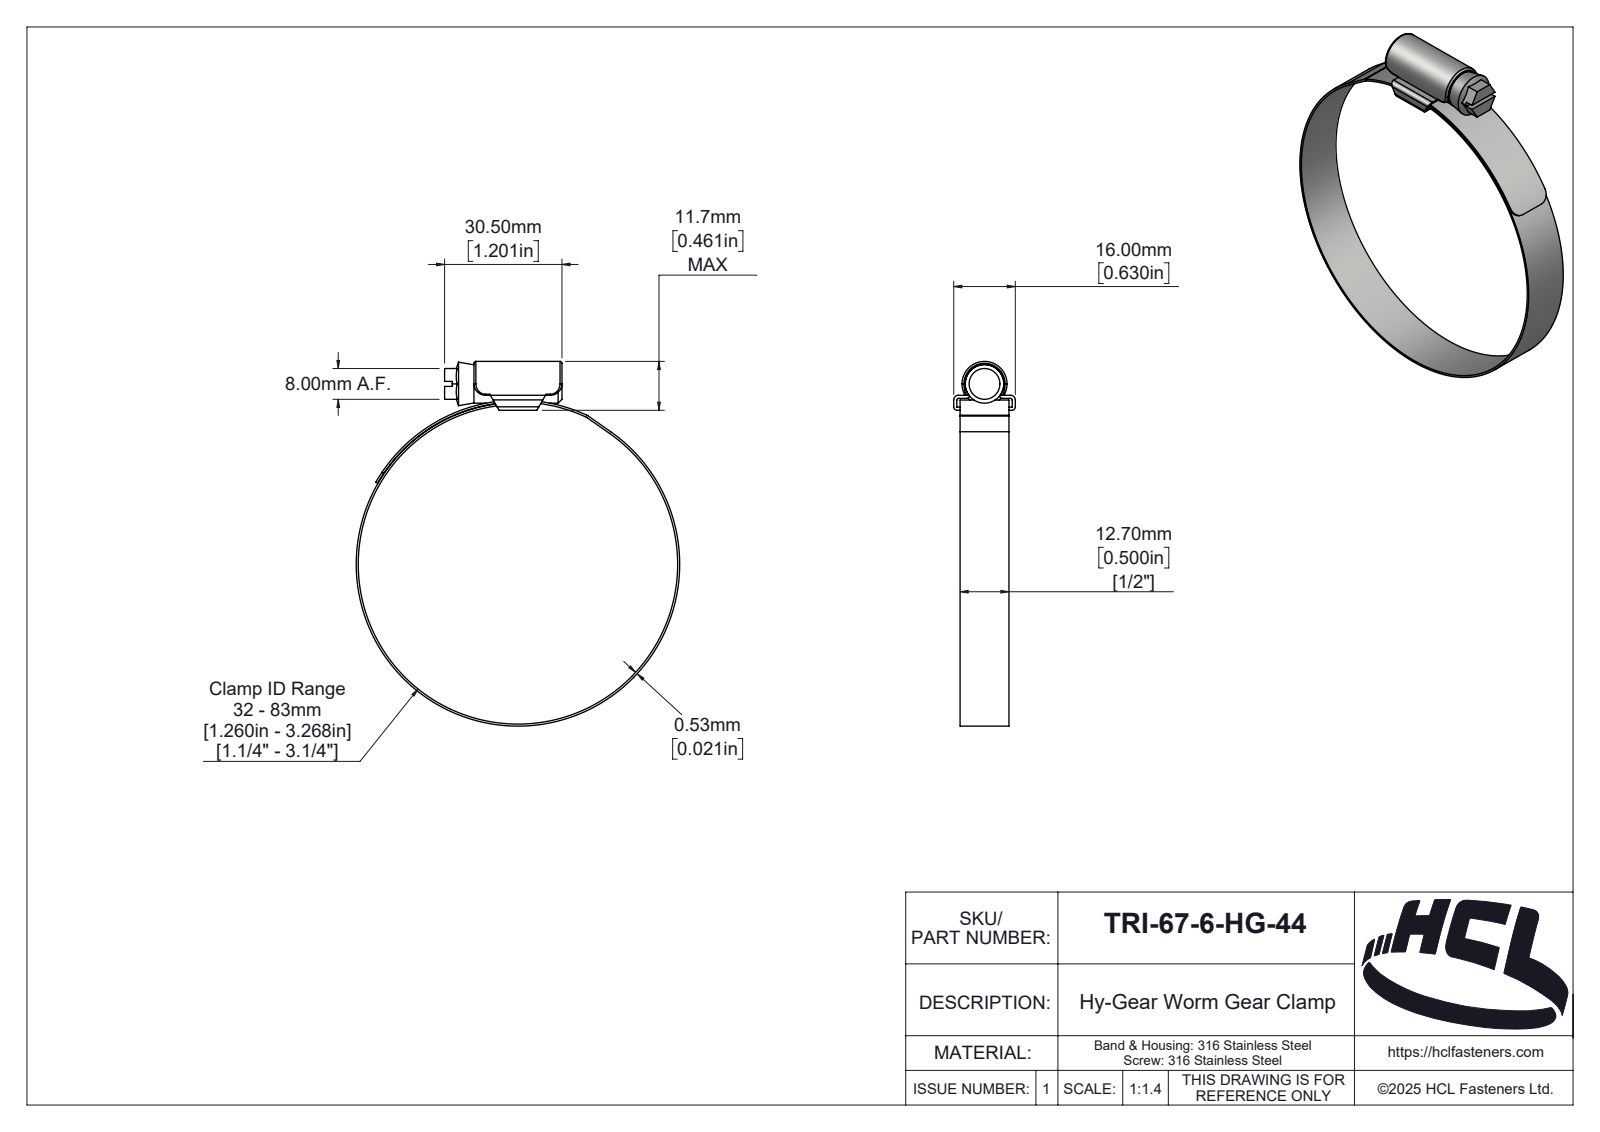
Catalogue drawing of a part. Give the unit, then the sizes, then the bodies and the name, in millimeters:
Units: millimetres
Overall size (bounding box): 94.73 × 84.06 × 16
Round holes (diameter × count): ⌀83 ×1
Round bosses / shafts (diameter × count): ⌀84.06 ×1, ⌀10 ×1
Partial cylindrical surfaces — rounded edges, fillets, slot ends (radius × count): R0.5 ×6, R3 ×4, R0.1 ×2, R0.9 ×2, R1.2 ×2, R0.46 ×1, R1.89 ×1, R2 ×1
Main face-to-face distances: 0.8, 12.7, 3.1, 0.53, 2.3, 3.9, 30.5, 1.65, 14.35, 15.2
Volume: 5 058 mm³ · Surface area: 11 031 mm²
Bodies: 3 solids, 189 faces (39 planar, 89 cylindrical, 61 other)
Part name (STEP PRODUCT): TRI-57-0-HG-44
STEP written by: SolidWorks 2025 (AUTOMOTIVE_DESIGN)
